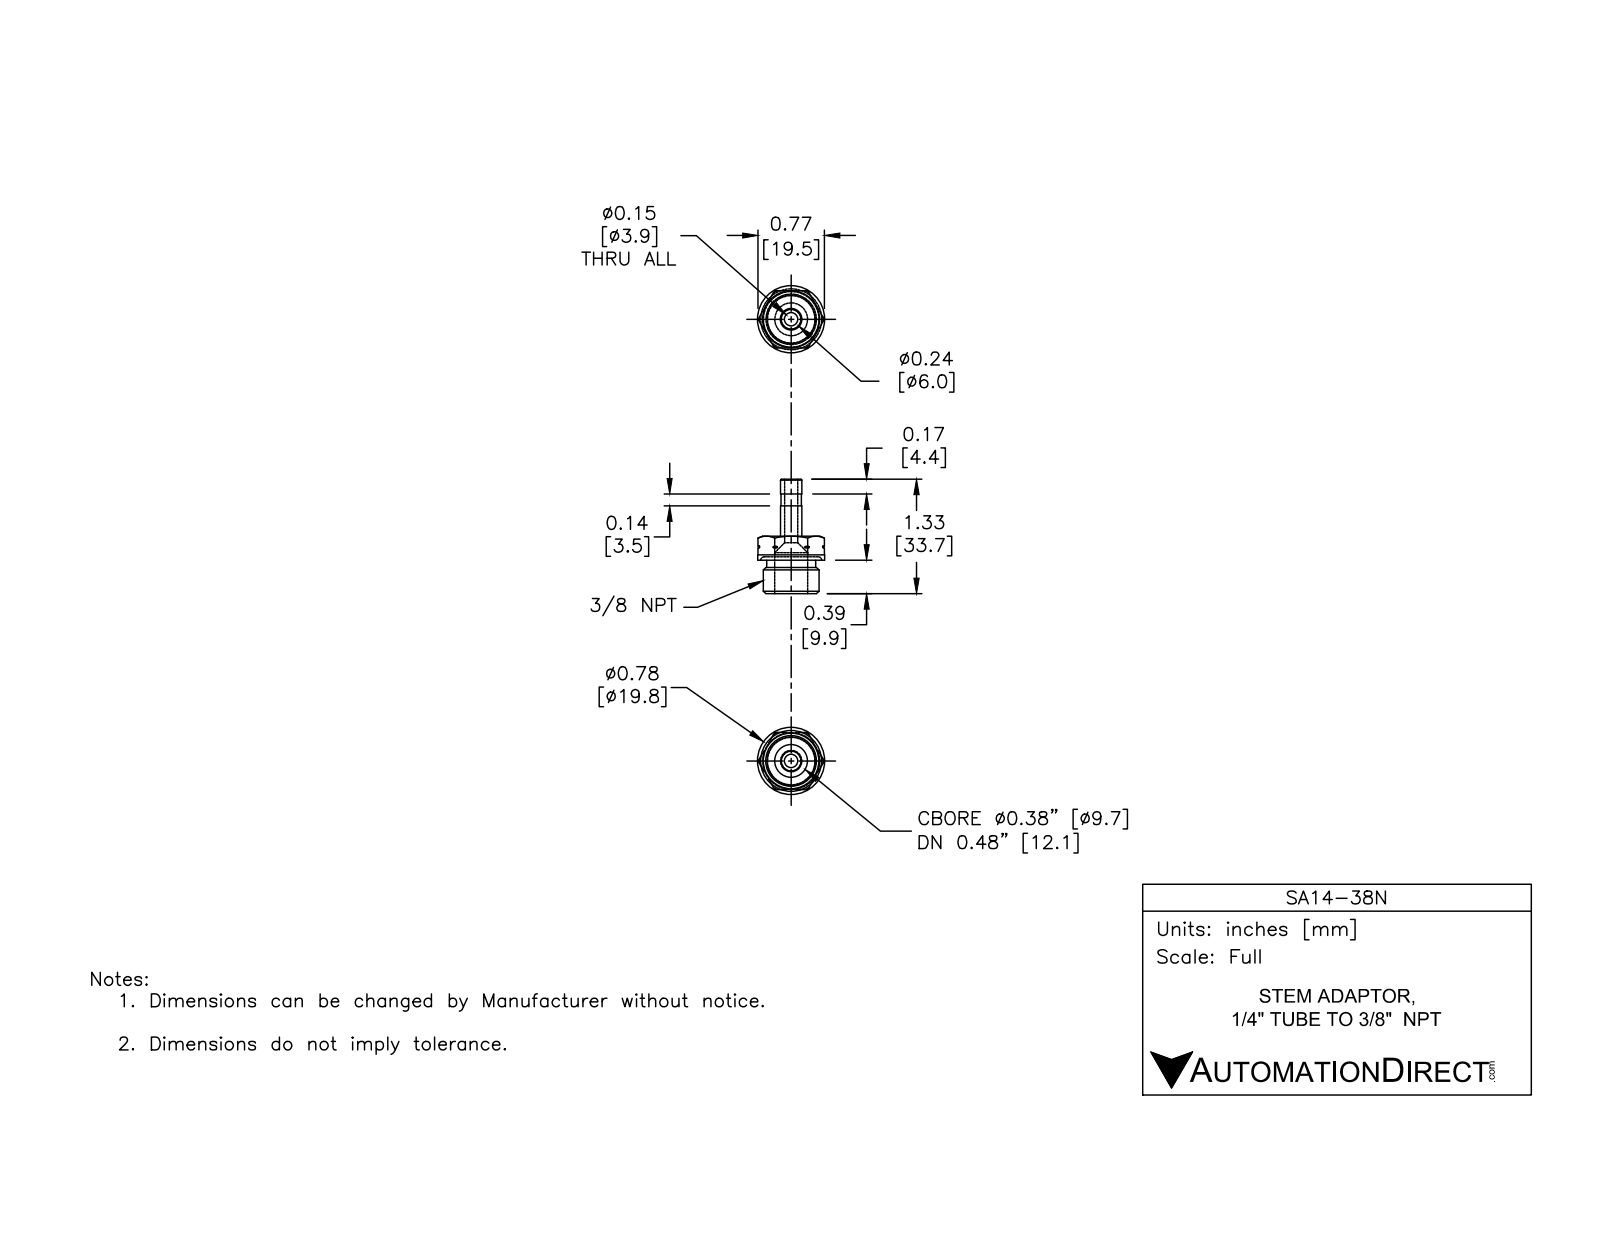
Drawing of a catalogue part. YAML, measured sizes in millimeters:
part_name: "SA14-38N"
step_written_by: "SolidWorks 2015 (CONFIG_CONTROL_DESIGN)"
units: millimeters
bodies: {solids: 2, faces: 62, planar: 14, cylindrical: 22, other: 26}
overall_size: [33.72, 19.75, 19.75]
volume: 3243
surface_area: 2820
round_holes:
  - {diameter: 3.91, count: 1}
  - {diameter: 9.7, count: 1}
round_bosses_or_shafts:
  - {diameter: 19.75, count: 1}
  - {diameter: 16.4, count: 1}
  - {diameter: 14.38, count: 1}
  - {diameter: 6.32, count: 1}
  - {diameter: 6.02, count: 1}
partial_cylinders:
  - {radius: 9.39, count: 1}
face_to_face_distances: [16.9, 7.12, 9.85, 16.97, 11.47, 1.62, 5.5, 33.72, 23.87, 22.25]
